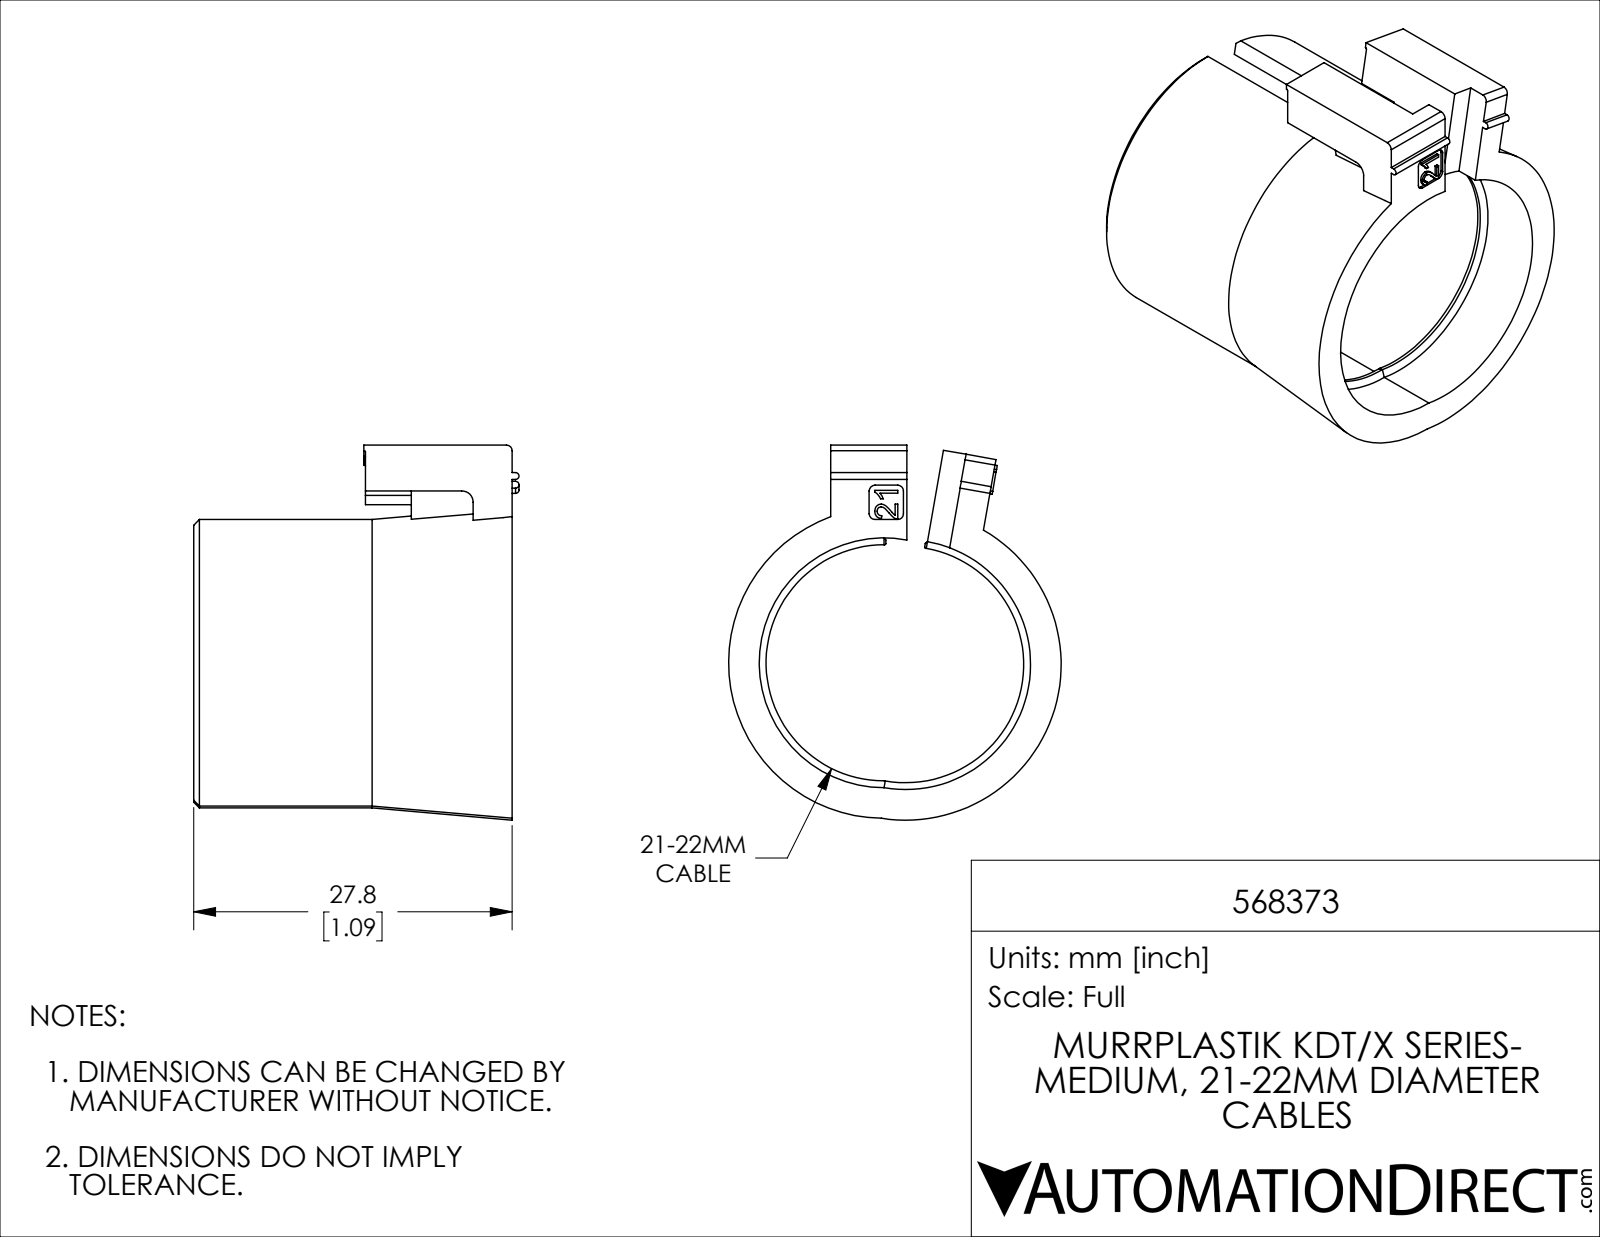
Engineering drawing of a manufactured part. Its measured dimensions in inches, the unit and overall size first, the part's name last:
Units: inches
Overall size (bounding box): 1.289 × 1.143 × 1.118
Partial cylindrical surfaces — rounded edges, fillets, slot ends (radius × count): R0.004 ×6, R0.02 ×6, R0.012 ×2, R0.039 ×2, R0.406 ×2, R0.429 ×2, R0.492 ×2
Main face-to-face distances: 1.094, 0.157, 0.183, 0.183, 0.079, 1.016, 0.504, 0.425, 0.591, 0.262
Volume: 0.269 in³ · Surface area: 7.935 in²
Bodies: 1 solid, 120 faces (70 planar, 27 cylindrical, 23 other)
Part name (STEP PRODUCT): 568373
STEP written by: SolidWorks 2019 (CONFIG_CONTROL_DESIGN)
